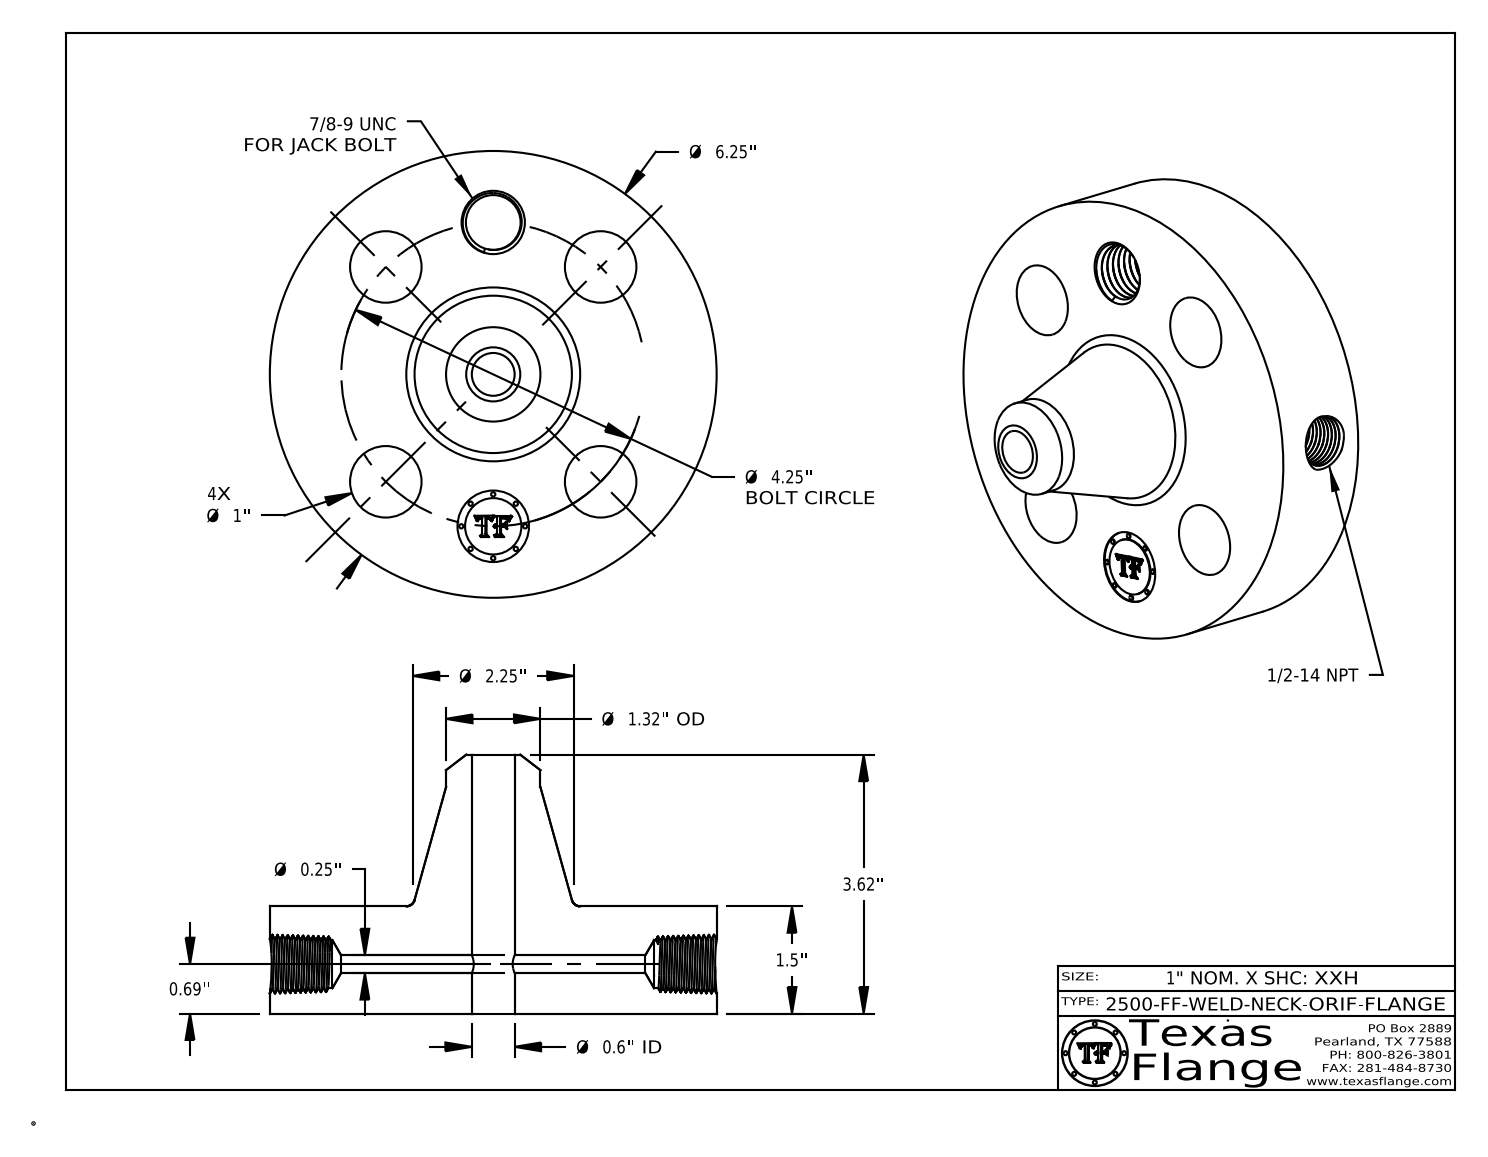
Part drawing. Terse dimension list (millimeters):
name: 2500-FF-WELD-NECK
written by: CATIA V5 STEP AP214 (AUTOMOTIVE_DESIGN)
unit: mm
bodies: 1 solid, 748 faces (368 planar, 80 cylindrical, 300 other)
size: 158.8 × 158.8 × 91.9
volume: 709 900 mm³; area: 85 160 mm²
holes: 5× ⌀25.4, 1× ⌀6.4, 1× ⌀15.2, 1× ⌀17.1, 1× ⌀19.5
bosses: 8× ⌀1.5, 1× ⌀158.8, 1× ⌀33.5, 1× ⌀20
face distances: 38.1, 0.4, 37.7, 91.9, 54.2, 53.8, 7.6, 7.4, 1.4, 6.3
hole spacings: 54, 41.3, 76.4, 99.7, 108
